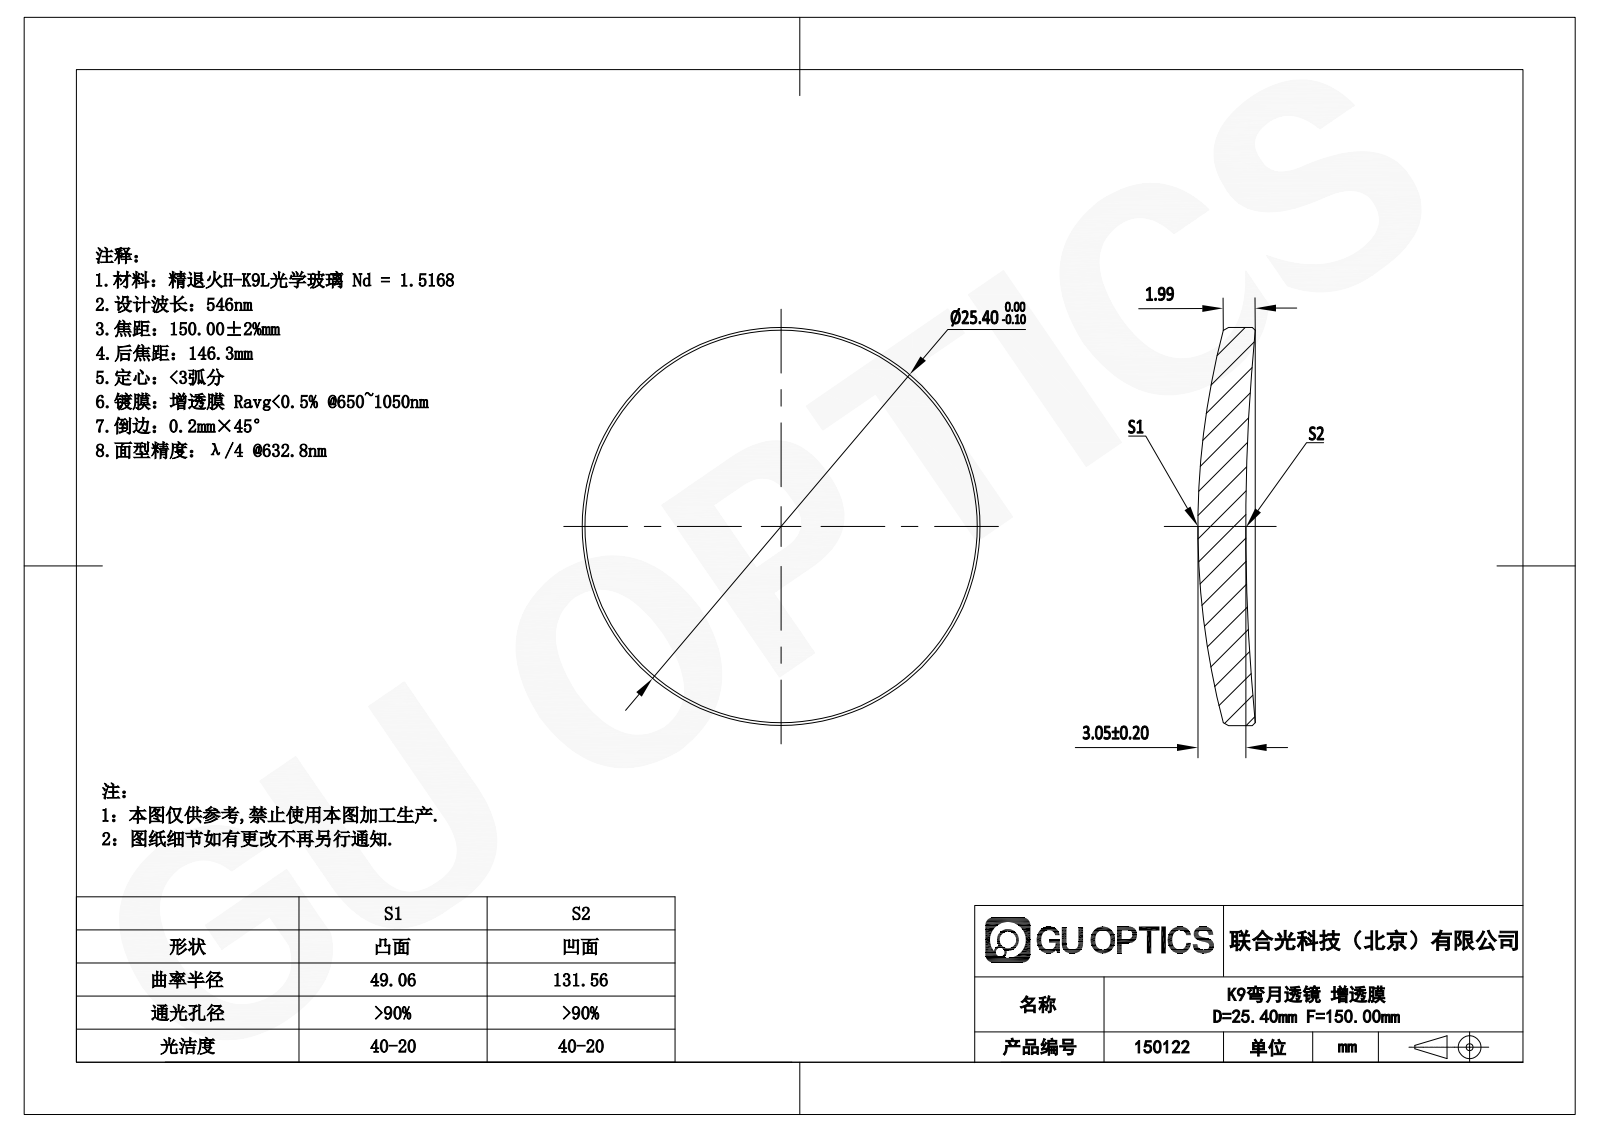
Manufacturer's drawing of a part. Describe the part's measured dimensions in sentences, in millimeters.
The part is named "GLM1-025B-150-NIR". Its 3-D file was written by "SolidWorks 2022 (AUTOMOTIVE_DESIGN)". It is 1 solid with 10 faces: 0 planar, 2 cylindrical and 8 other. Overall it measures 25.4 by 25.4 by 3.65 millimeters. Its volume is 1 280 cubic millimeters and its surface area 1 165 square millimeters. Round bosses or shafts: 1 of diameter 25.4.
